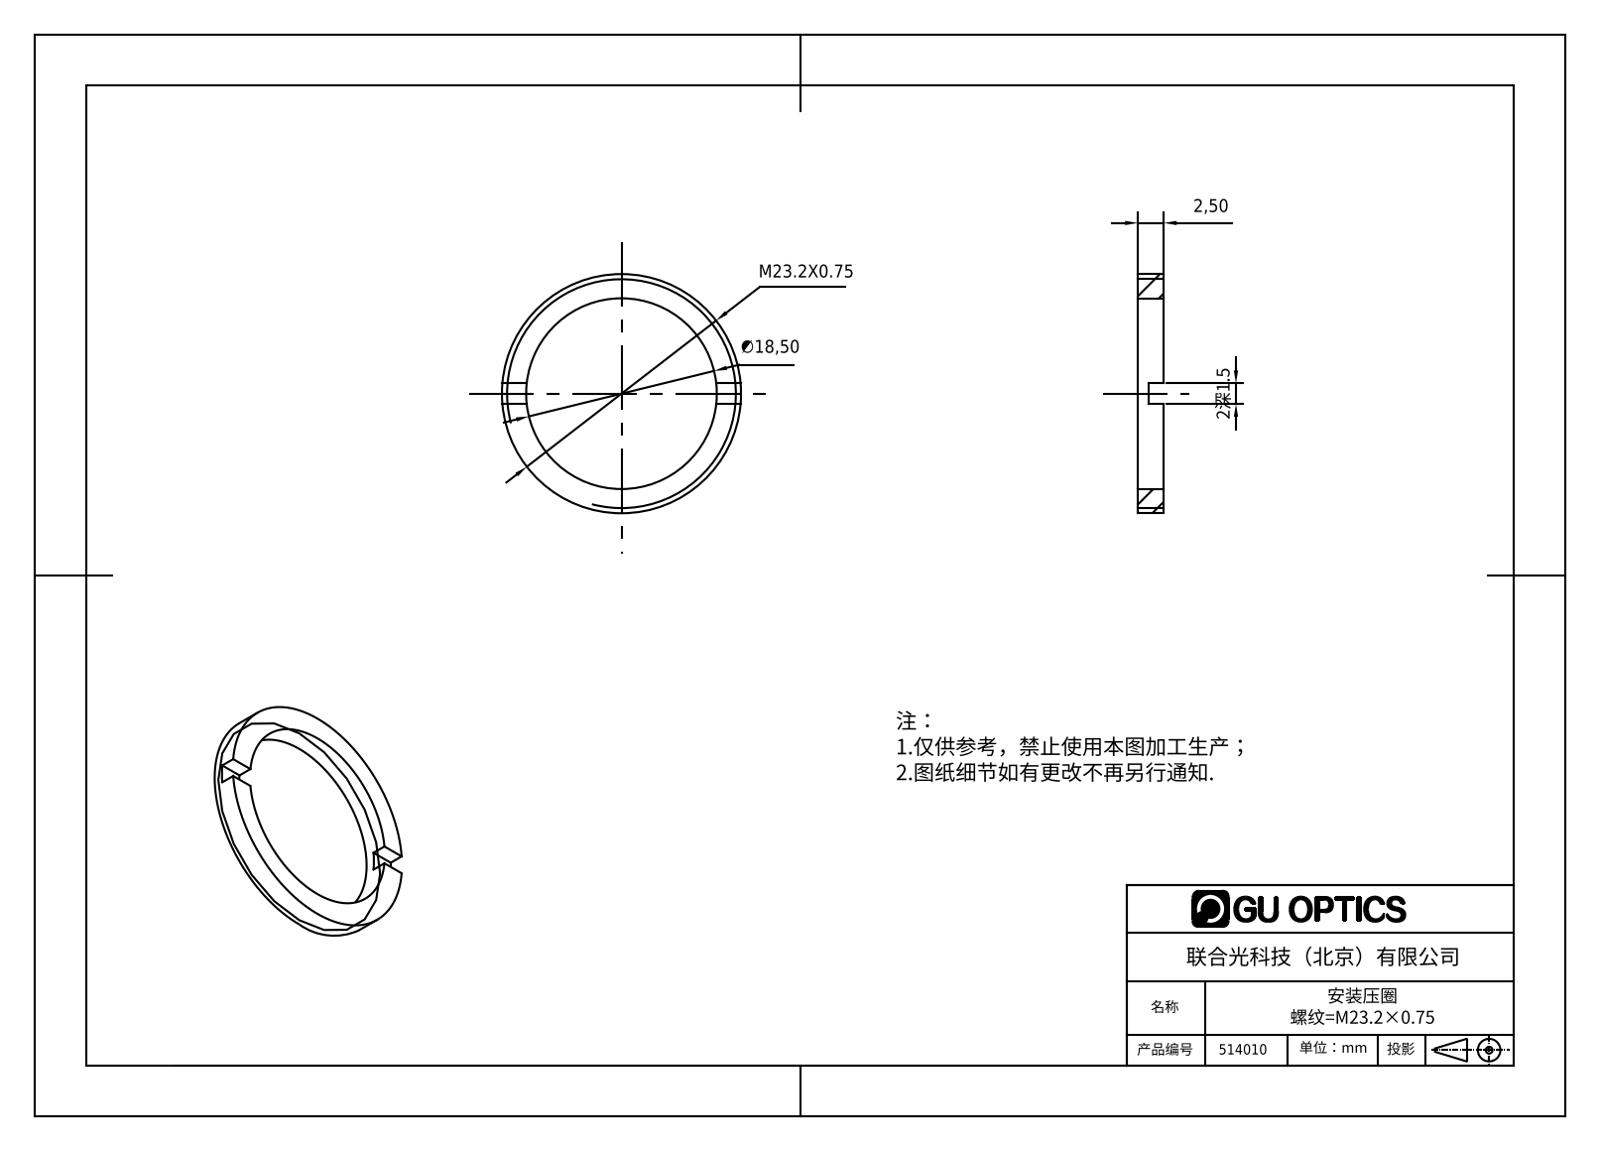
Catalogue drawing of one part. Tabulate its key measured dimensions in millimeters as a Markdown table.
| quantity | value |
| --- | --- |
| part name | 514010 |
| STEP written by | SolidWorks 2016 (CONFIG_CONTROL_DESIGN) |
| units | millimeters |
| bodies | 1 solid, 13 faces (9 planar, 4 cylindrical, 0 other) |
| overall size | 23.2 × 23.2 × 2.5 |
| volume | 371 mm³ |
| surface area | 638 mm² |
| round holes (diameter × count) | 18.5 × 1 |
| round bosses / shafts (diameter × count) | 23.2 × 1 |
| main face-to-face distances | 2.5, 1, 1.5, 2 |
